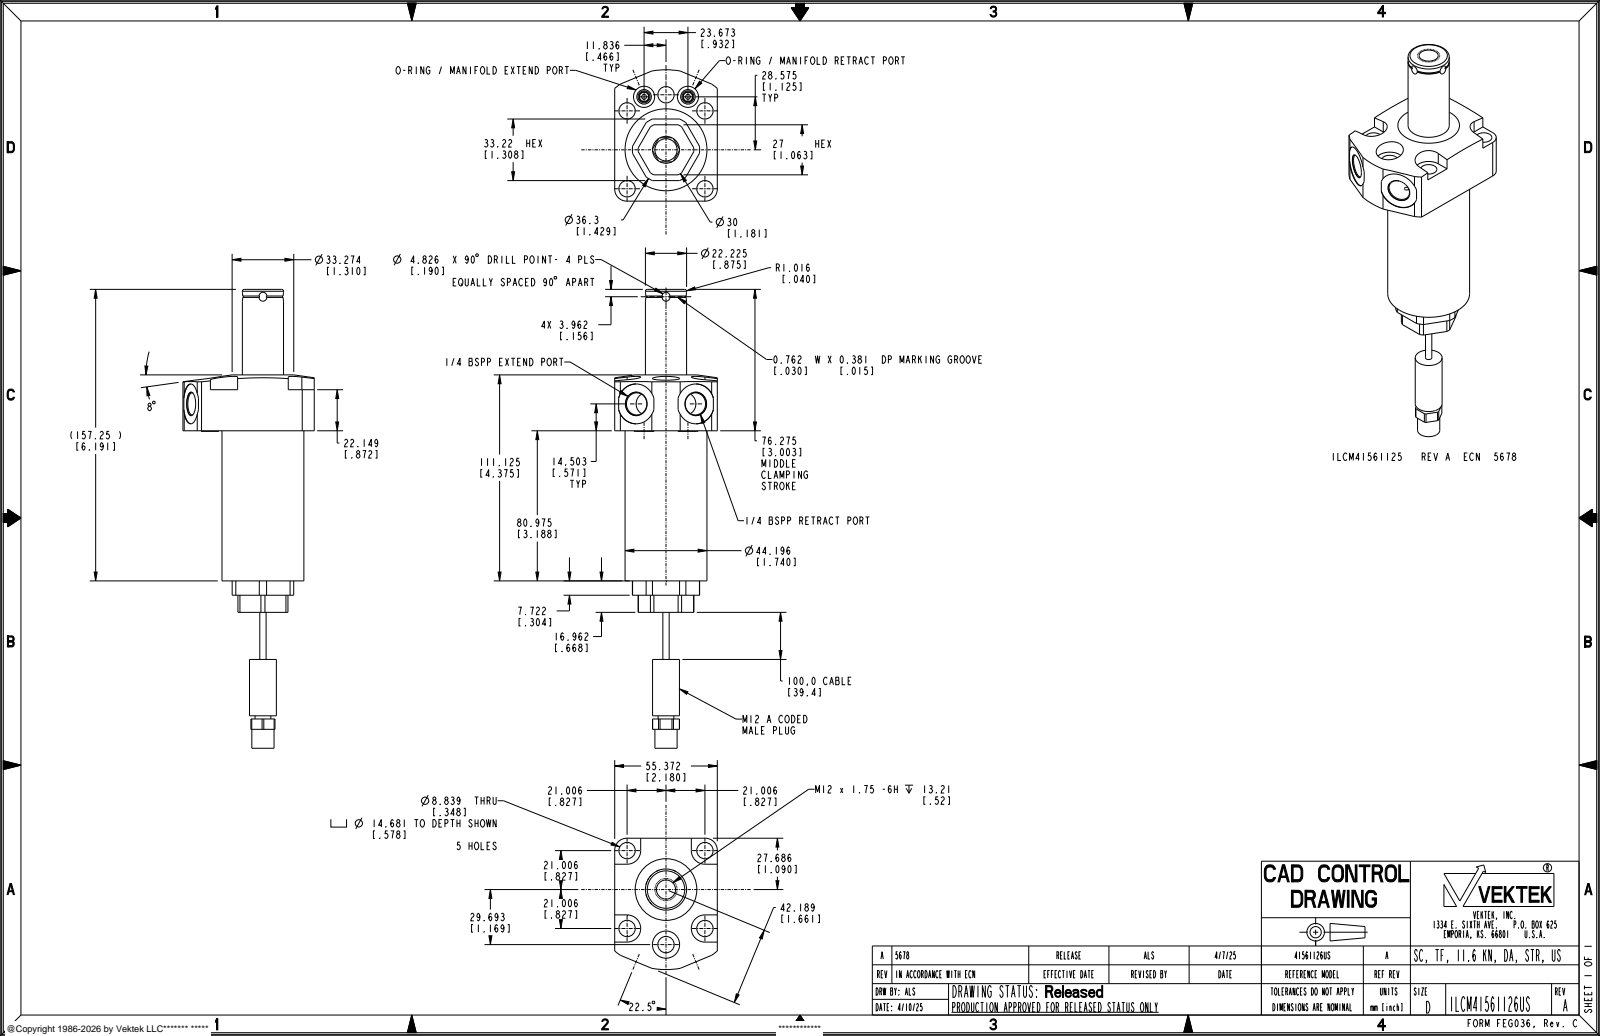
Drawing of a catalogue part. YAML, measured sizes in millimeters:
part_name: "ILCM41561126US"
step_written_by: "CREO PARAMETRIC BY PTC INC, 2021164 (AUTOMOTIVE_DESIGN)"
units: millimeters
bodies: {solids: 1, faces: 205, planar: 88, cylindrical: 87, other: 30}
overall_size: [247.52, 77.22, 60.45]
volume: 251766
surface_area: 39729
round_holes:
  - {diameter: 8.84, count: 5}
  - {diameter: 2.49, count: 2}
  - {diameter: 6.5, count: 2}
  - {diameter: 11.4, count: 2}
  - {diameter: 11.89, count: 2}
  - {diameter: 21.5, count: 2}
  - {diameter: 10.31, count: 1}
  - {diameter: 14.68, count: 1}
  - {diameter: 22.73, count: 1}
round_bosses_or_shafts:
  - {diameter: 5.49, count: 2}
  - {diameter: 44.2, count: 1}
  - {diameter: 22.23, count: 1}
  - {diameter: 14.5, count: 1}
  - {diameter: 11.99, count: 1}
  - {diameter: 11.99, count: 1}
  - {diameter: 8.51, count: 1}
  - {diameter: 3.4, count: 1}
partial_cylinders:
  - {radius: 7.34, count: 4}
  - {radius: 6.48, count: 2}
  - {radius: 10.73, count: 1}
  - {radius: 15, count: 1}
  - {radius: 18.15, count: 1}
  - {radius: 43.18, count: 1}
face_to_face_distances: [55.38, 80.97, 3.11, 30.11, 16.97, 97.94, 120.09, 103.12, 22.15, 128.09]
hole_center_spacings: [29.71, 42.02, 11.88, 11.89, 22.73, 30.93, 33.71, 50.42]
